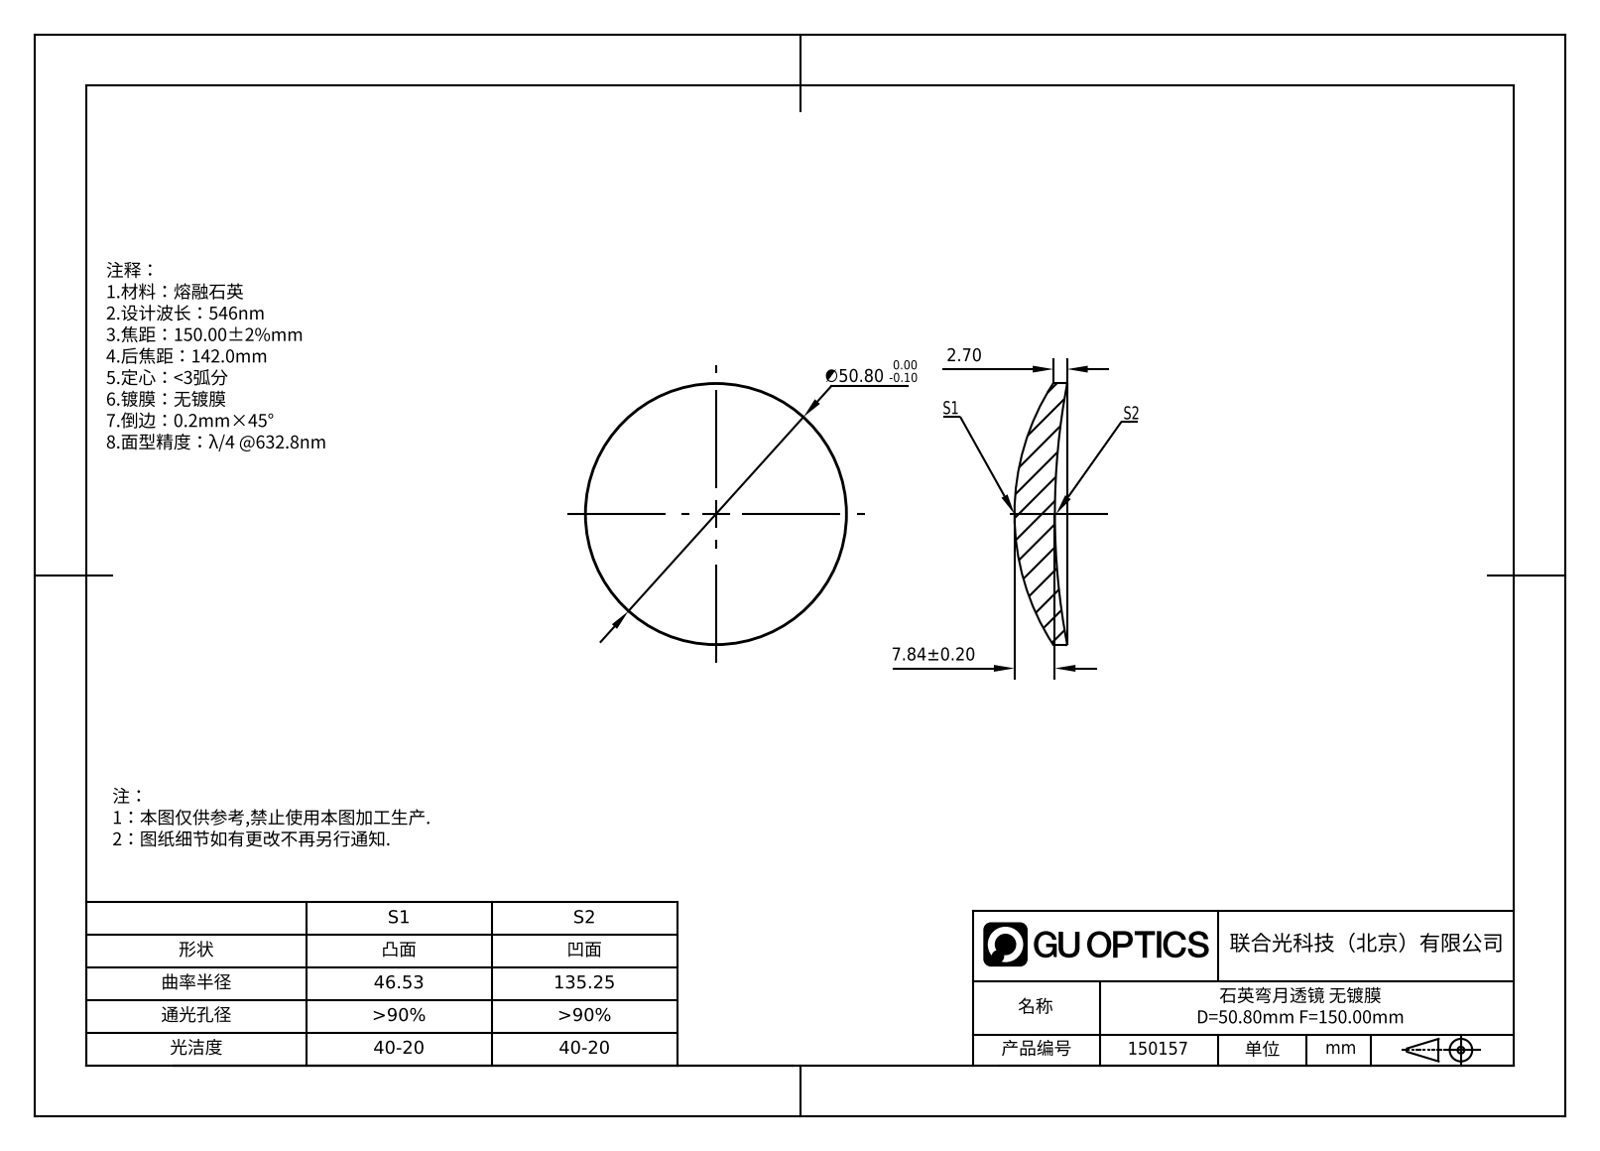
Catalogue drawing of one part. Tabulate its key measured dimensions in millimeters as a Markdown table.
| quantity | value |
| --- | --- |
| part name | GLM2-050B-150 |
| STEP written by | SolidWorks 2022 (AUTOMOTIVE_DESIGN) |
| units | millimeters |
| bodies | 1 solid, 8 faces (0 planar, 2 cylindrical, 6 other) |
| overall size | 50.8 × 50.8 × 10.21 |
| volume | 10 894 mm³ |
| surface area | 4 660 mm² |
| round bosses / shafts (diameter × count) | 50.8 × 1 |
